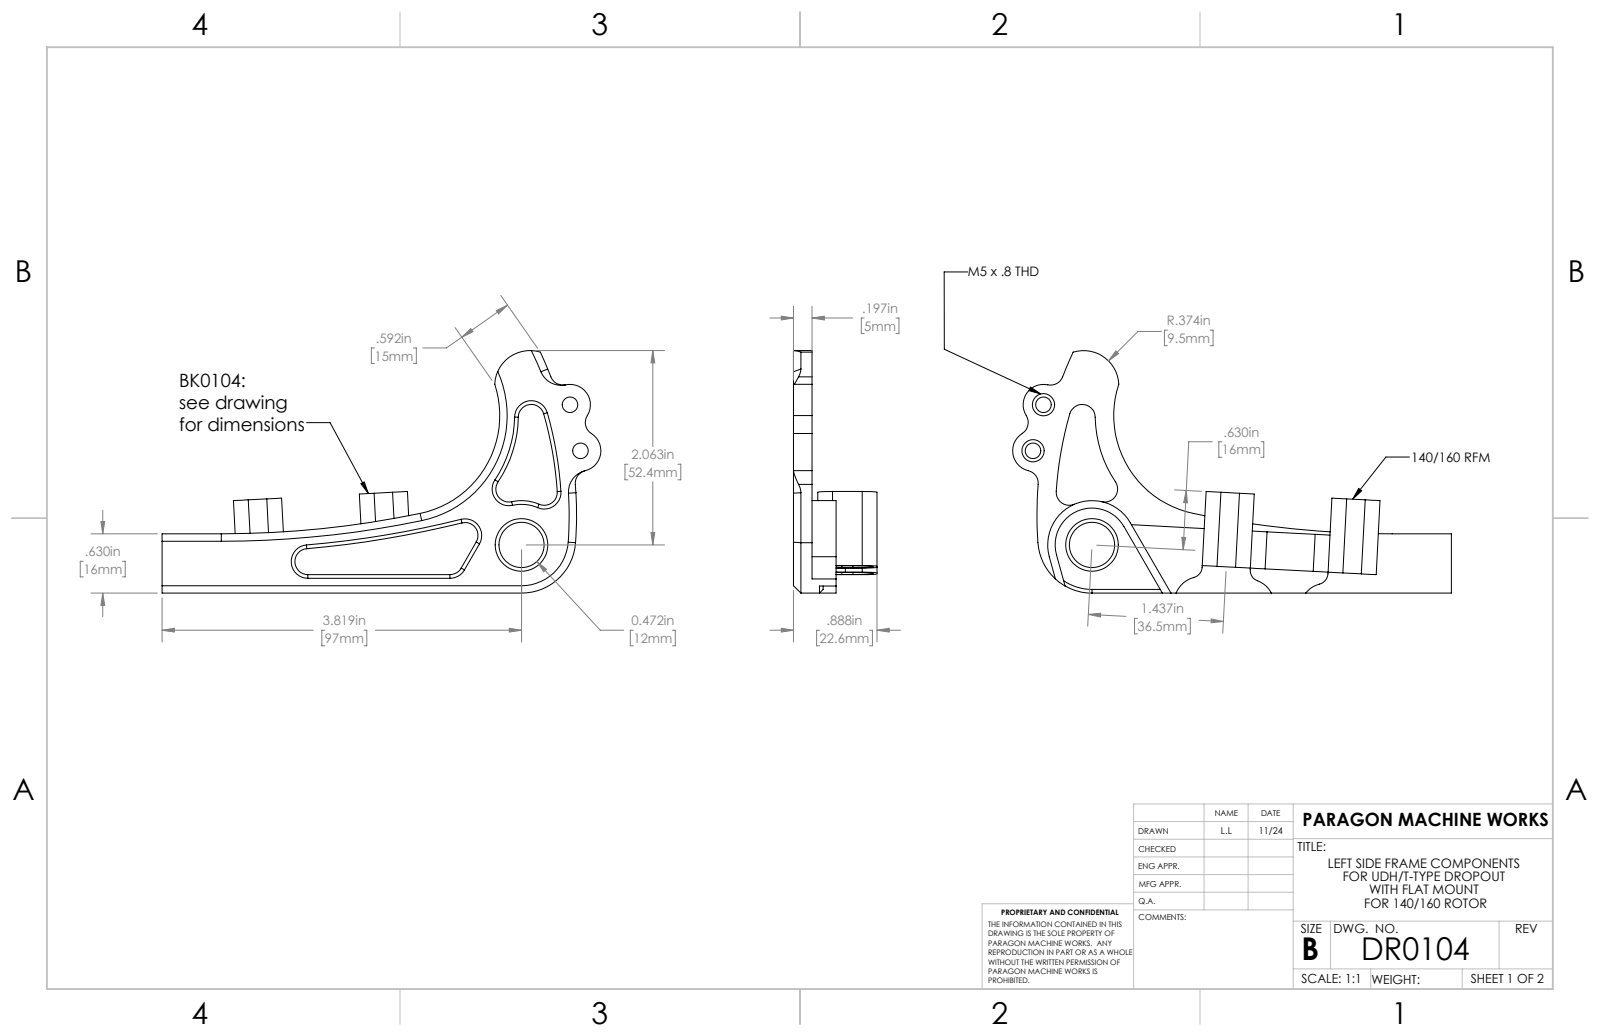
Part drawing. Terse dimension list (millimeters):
name: DR0104L
written by: SolidWorks 2023 (AUTOMOTIVE_DESIGN)
unit: mm
bodies: 1 solid, 96 faces (26 planar, 41 cylindrical, 29 other)
size: 118.42 × 65.41 × 11.5
volume: 14 700 mm³; area: 8 538 mm²
holes: 2× ⌀4.2, 1× ⌀12.2
rounds: 9× R3.5, 3× R3, 3× R7, 2× R5.5, 1× R9.5, 1× R9.95, 1× R11.95, 1× R14.63
face distances: 5, 3, 8, 2, 6, 11.5, 9.5, 6.5, 3.5, 10
hole spacings: 12.74, 29.96, 40
